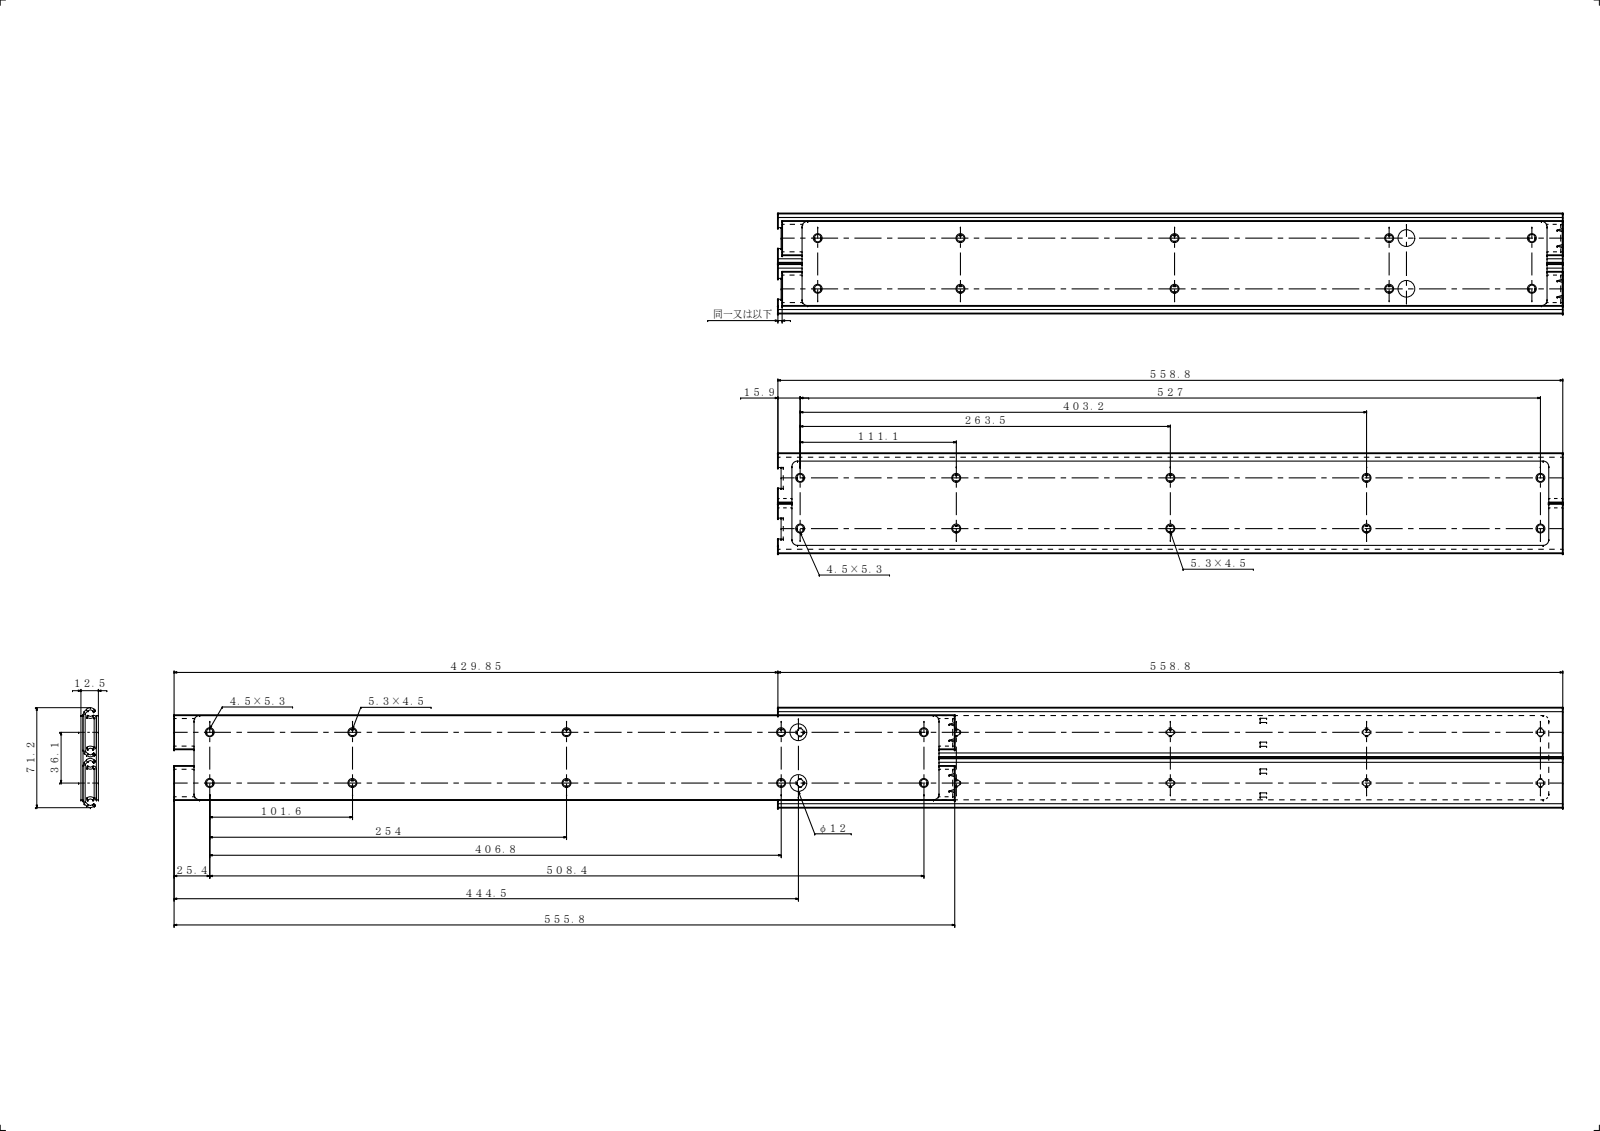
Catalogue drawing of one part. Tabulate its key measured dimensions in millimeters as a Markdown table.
| quantity | value |
| --- | --- |
| part name | OM-22継板; OM U61-22; IM-22継板; U61_22 (+1 more) |
| STEP written by | SolidWorks 2019 (CONFIG_CONTROL_DESIGN) |
| units | millimeters |
| bodies | 6 solids, 342 faces (148 planar, 194 cylindrical, 0 other) |
| overall size | 988.65 × 71.2 × 12.5 |
| volume | 226 568 mm³ |
| surface area | 314 127 mm² |
| round holes (diameter × count) | 6.4 × 24, 12 × 2 |
| partial cylindrical surfaces (radius × count) | 2.25 × 40, 0.4 × 12, 1 × 12, 3 × 12, 2 × 8, 3.2 × 8, 4 × 8, 0.3 × 4 |
| main face-to-face distances | 1.5, 9.5, 11, 3, 8, 12.5, 6.5, 25.52, 25.53, 25.59 |
| hole center spacings | 36.1, 50.8, 62.32, 429.85, 431.36, 101.6, 107.82, 152.4 |
